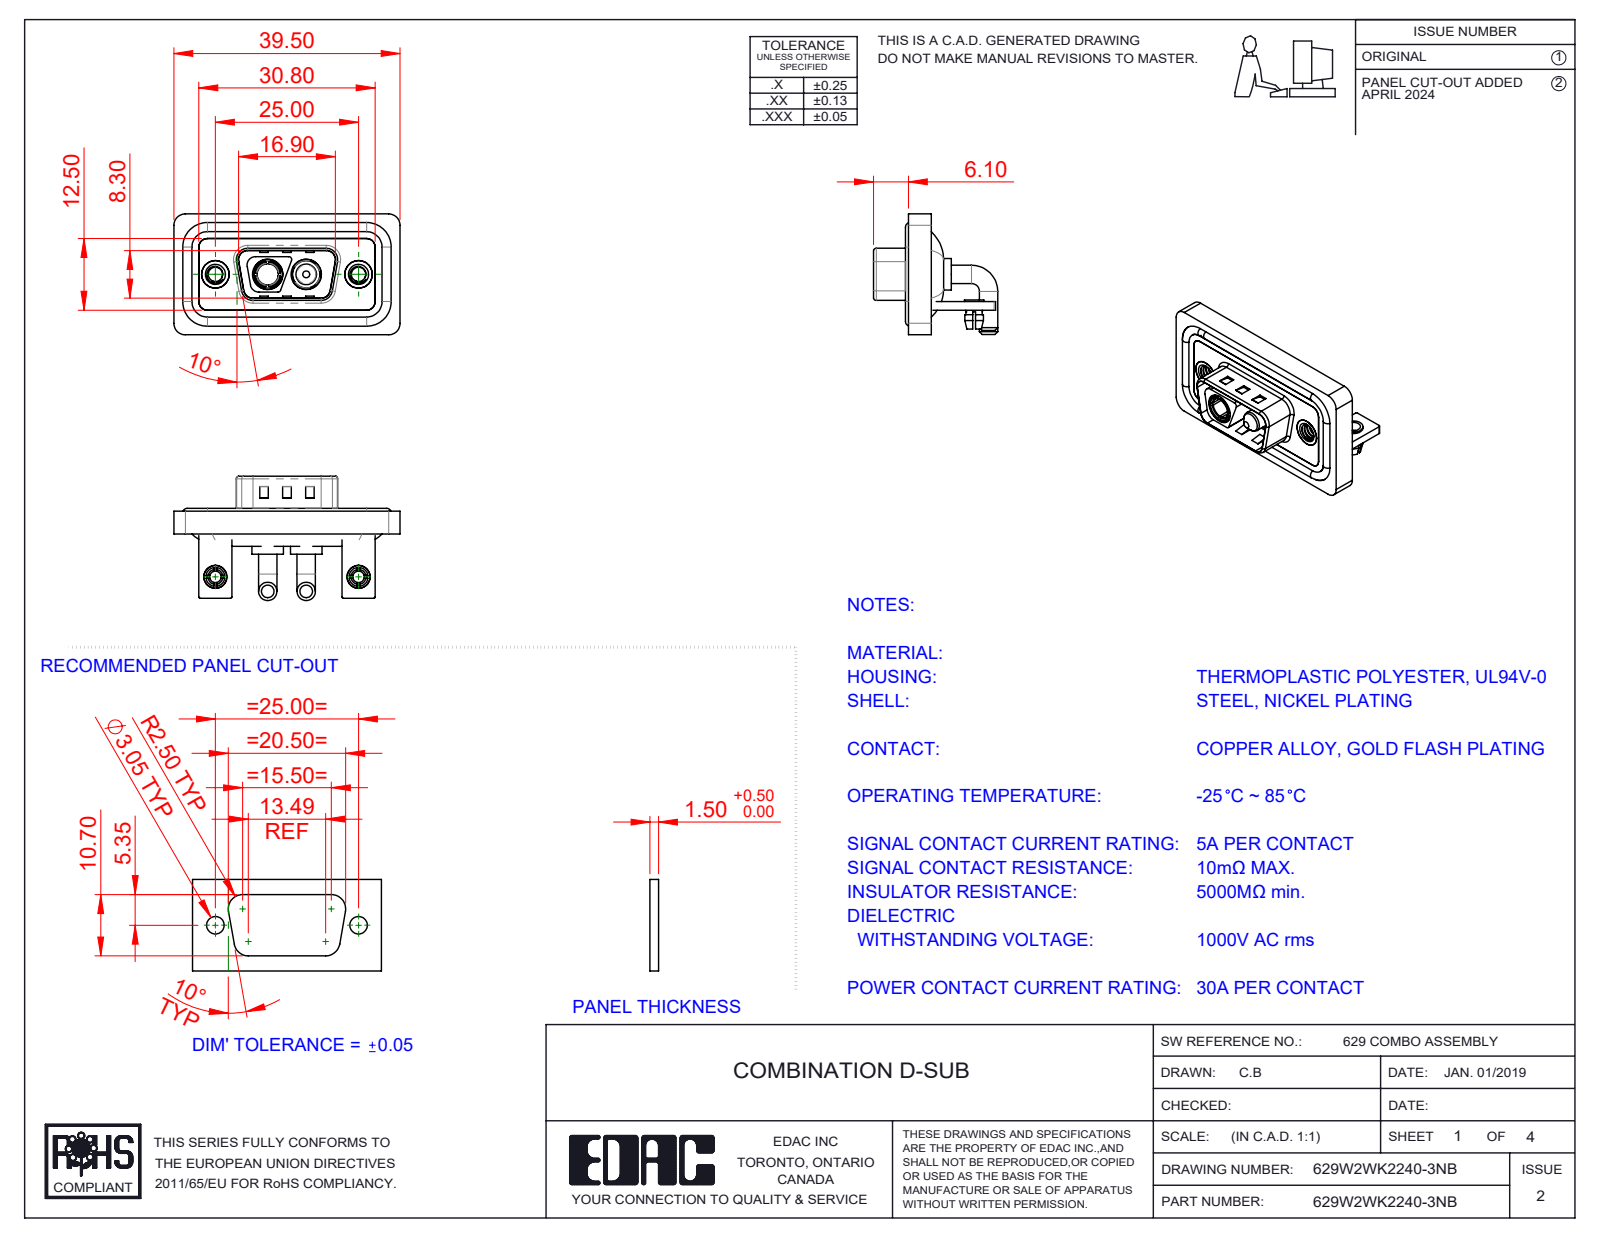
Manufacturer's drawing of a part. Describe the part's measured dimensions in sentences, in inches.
The part is named "629Combo Waterproof Housing_09 Contacts; 629Combo Threaded Rivet_B; 629Combo Board Lock; 629W2WK2240-3NB (+6 more)". Its 3-D file was written by "SolidWorks 2023 (CONFIG_CONTROL_DESIGN)". It is 15 solids with 672 faces: 257 planar, 281 cylindrical and 134 other. Overall it measures 1.555 by 0.854 by 0.831 inches. Its volume is 0.308 cubic inches and its surface area 12.97 square inches. Round holes: 4 of diameter 0.098, 2 of diameter 0.079, 2 of diameter 0.126, 2 of diameter 0.157, 2 of diameter 0.189, 2 of diameter 0.191, 2 of diameter 0.197, 2 of diameter 0.209, 1 of diameter 0.146. Round bosses or shafts: 4 of diameter 0.126, 4 of diameter 0.063, 2 of diameter 0.217, 2 of diameter 0.205, 2 of diameter 0.193, 2 of diameter 0.187, 2 of diameter 0.157, 2 of diameter 0.148. Partial cylindrical surfaces (rounded edges, fillets, slot ends): 20 of radius 0.059, 19 of radius 0.079, 16 of radius 0.01, 11 of radius 0.02, 8 of radius 0.063, 4 of radius 0.024, 4 of radius 0.026, 4 of radius 0.035. The main face-to-face distances are 0.016, 0.059, 0.114, 0.031, 0.043, 0.047, 0.083, 0.063, 0.146, 0.098. The hole center spacings are 0.36, 0.624, 0.984, 0.265.
